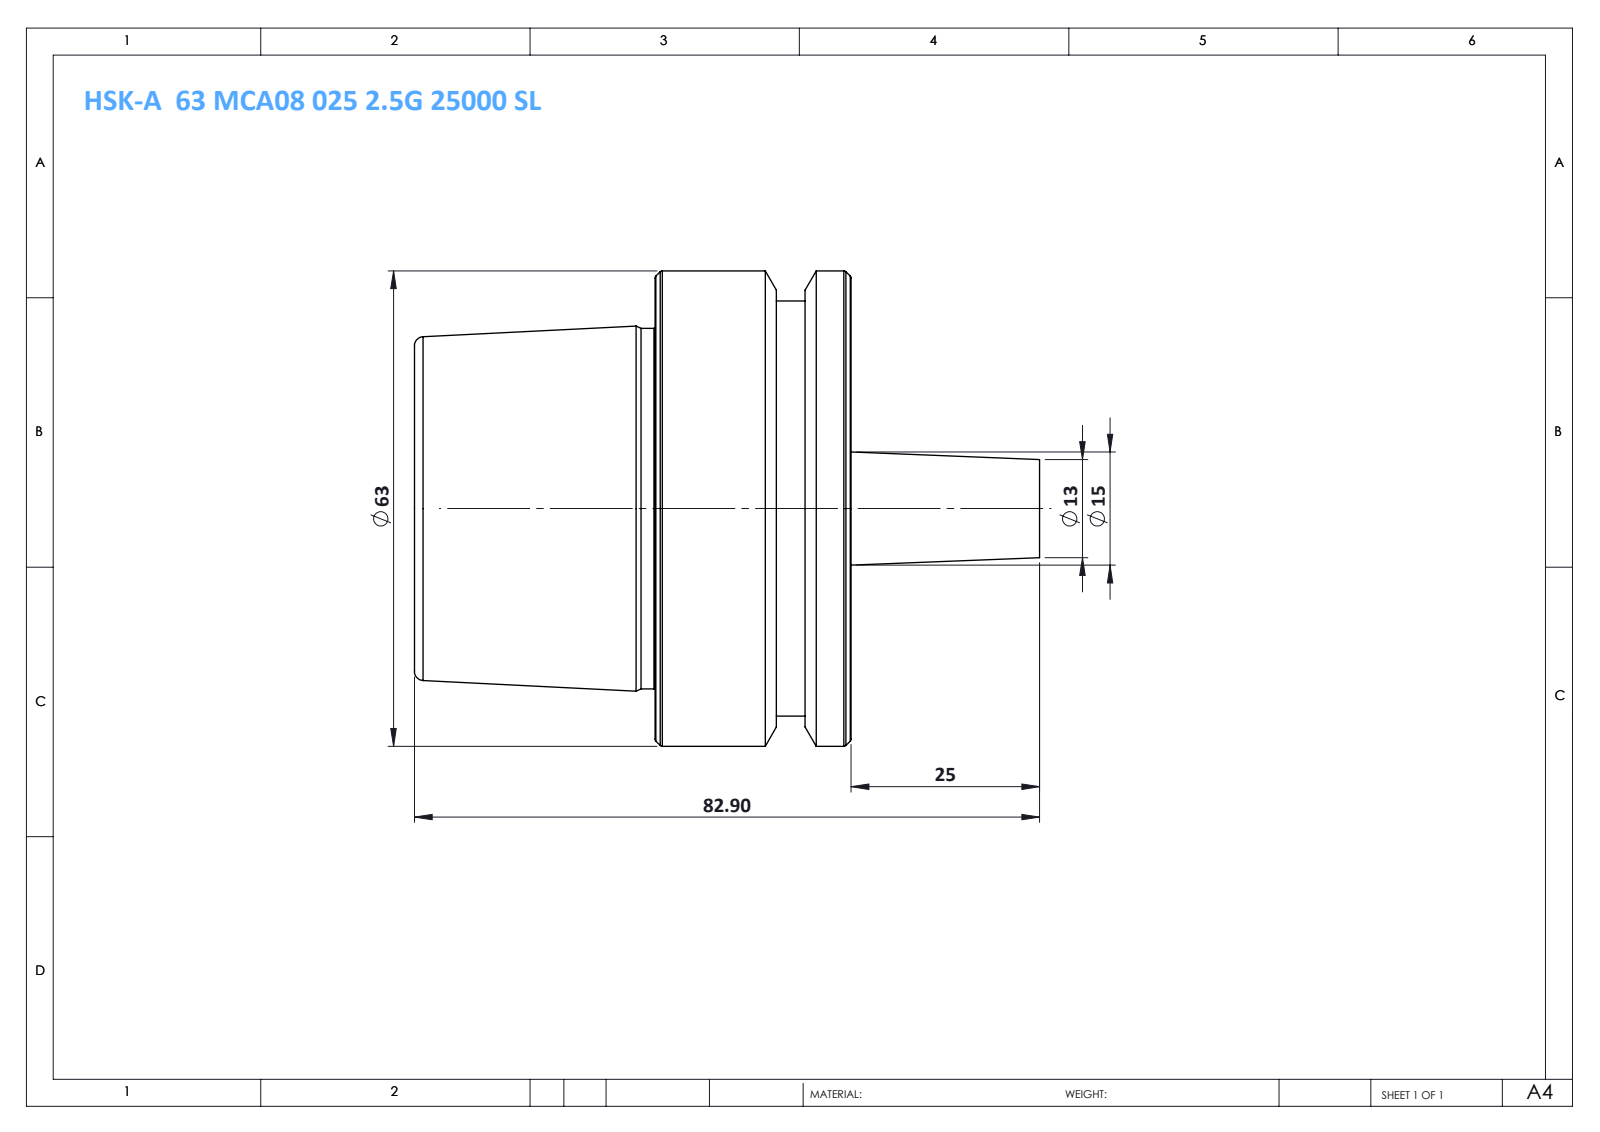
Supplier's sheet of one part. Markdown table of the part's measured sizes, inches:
| quantity | value |
| --- | --- |
| part name | HSK-A 63 MCA08 025 2.5G 25000 SL |
| STEP written by | SolidWorks 2014 (CONFIG_CONTROL_DESIGN) |
| units | inches |
| bodies | 1 solid, 42 faces (6 planar, 8 cylindrical, 28 other) |
| overall size | 3.264 × 2.48 × 2.48 |
| volume | 8.327 in³ |
| surface area | 27.44 in² |
| round bosses / shafts (diameter × count) | 2.48 × 1, 2.165 × 1, 1.881 × 1 |
| main face-to-face distances | 2.28, 1.024, 1.256, 0.24, 0.783, 2.039, 0.39, 0.15, 0.634, 1.89 |
